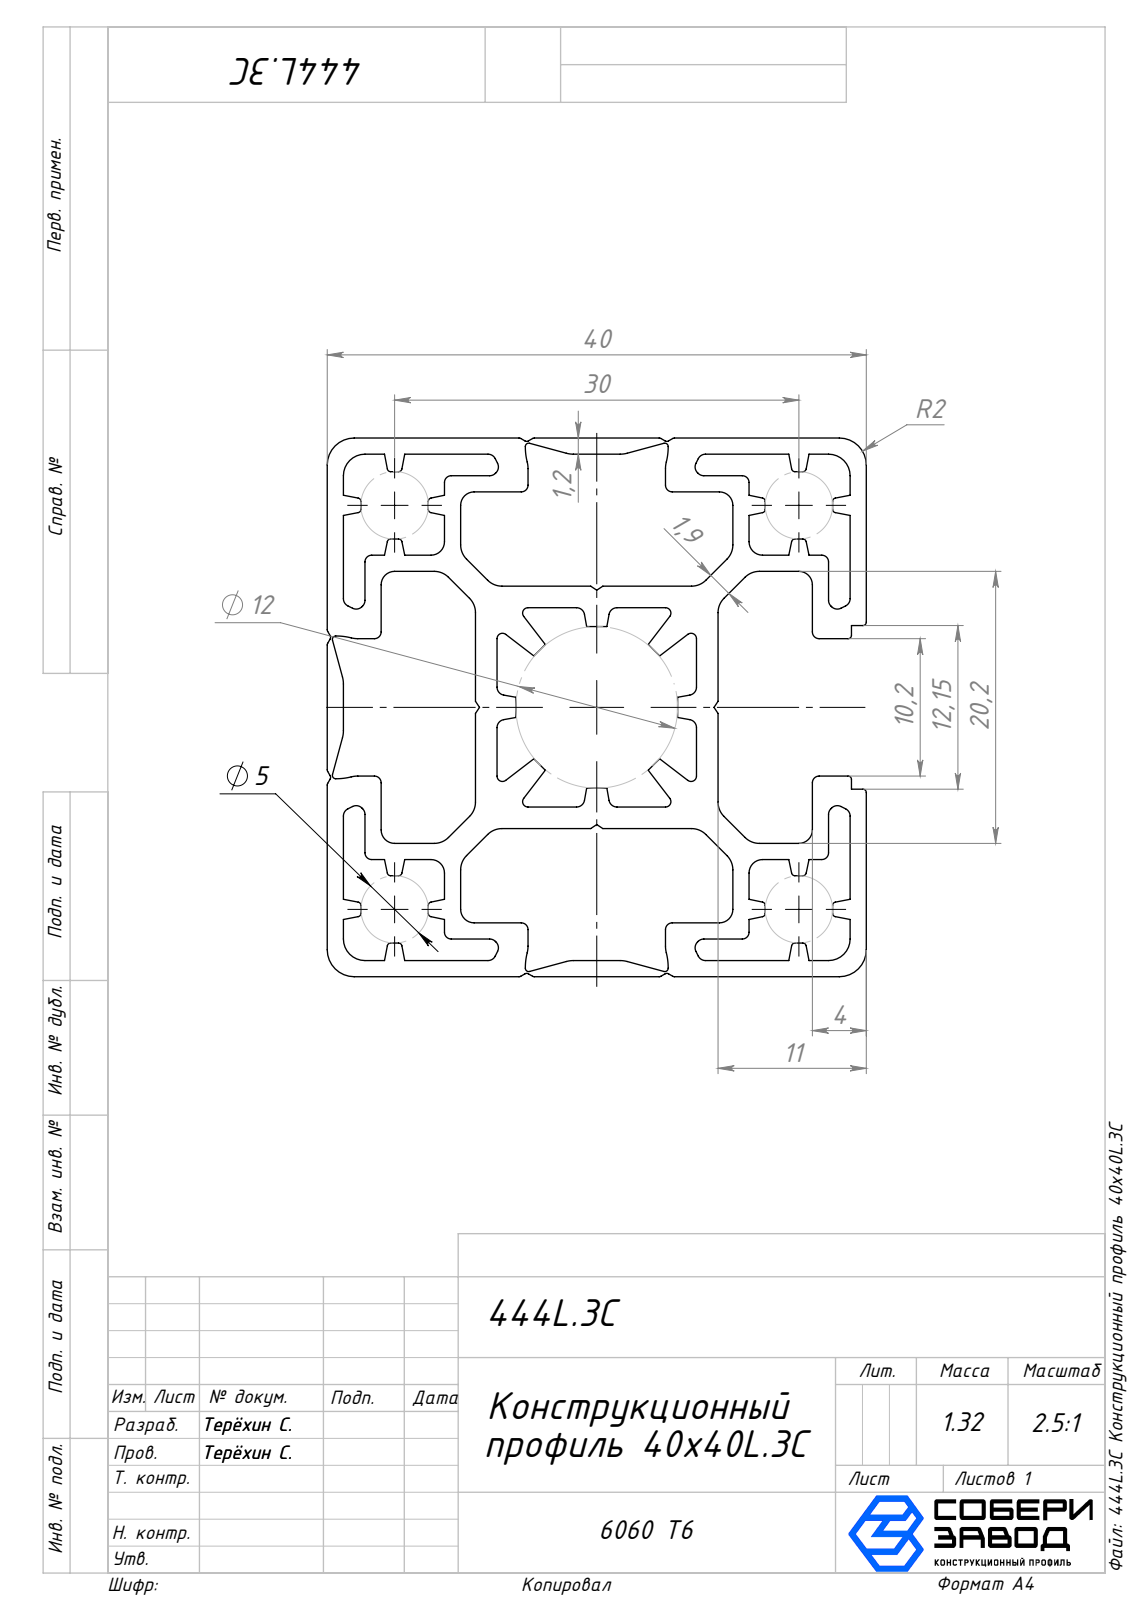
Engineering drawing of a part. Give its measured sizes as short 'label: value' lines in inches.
name: 444L.3C Конструкционный профиль 40х40L.3C_00; 444L.3C Конструкционный профиль 40х40L.3C
written by: SolidWorks 2025 (CONFIG_CONTROL_DESIGN)
unit: in
bodies: 1 solid, 408 faces (222 planar, 186 cylindrical, 0 other)
size: 39.37 × 1.575 × 1.575
volume: 29.92 in³; area: 1 014 in²
rounds: 60× R0.01, 32× R0.024, 16× R0.02, 16× R0.059, 16× R0.079, 12× R0.039, 8× R0.016, 6× R0.18
face distances: 0.047, 0.386, 1.528, 1.575, 0.433, 1.142, 1.094, 1.031, 0.063, 0.11
